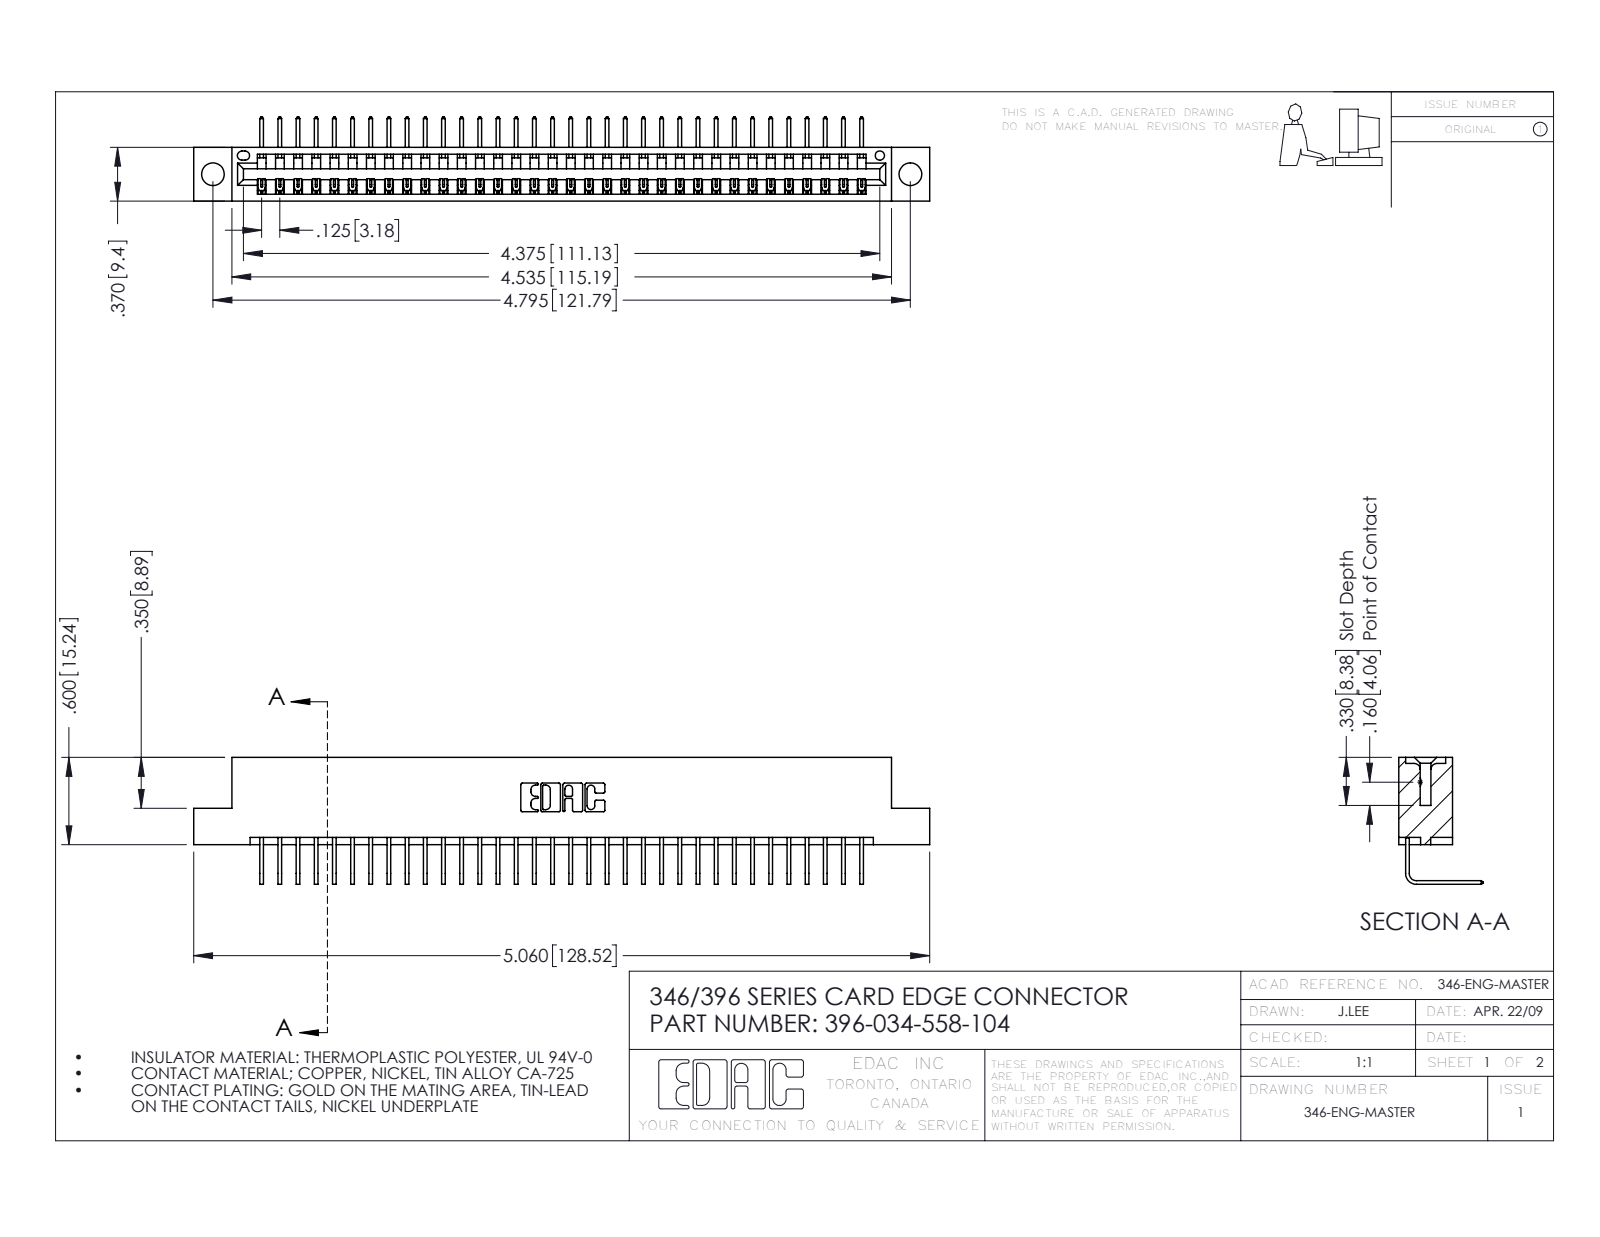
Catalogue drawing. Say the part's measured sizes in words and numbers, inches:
The part is named "345-292-001_558 Tail - 2; 396-034-558-104; 346 Part_Flush Mounting Lugs - 0.156 Dia-TH". Its 3-D file was written by "SolidWorks 2016 (CONFIG_CONTROL_DESIGN)". It is 35 solids with 2162 faces: 1504 planar, 658 cylindrical and 0 other. Overall it measures 5.06 by 0.873 by 0.58 inches. Its volume is 0.749 cubic inches and its surface area 24.39 square inches. Round holes: 2 of diameter 0.156, 1 of diameter 0.064. Partial cylindrical surfaces (rounded edges, fillets, slot ends): 68 of radius 0.006, 22 of radius 0.01, 6 of radius 0.007, 6 of radius 0.031, 3 of radius 0.026, 2 of radius 0.031, 2 of radius 0.04, 1 of radius 0.014. The main face-to-face distances are 0.322, 0.048, 0.37, 0.25, 0.298, 0.025, 0.072, 0.148, 0.222, 0.1. The hole center spacings are 0.246, 4.587, 4.795.
